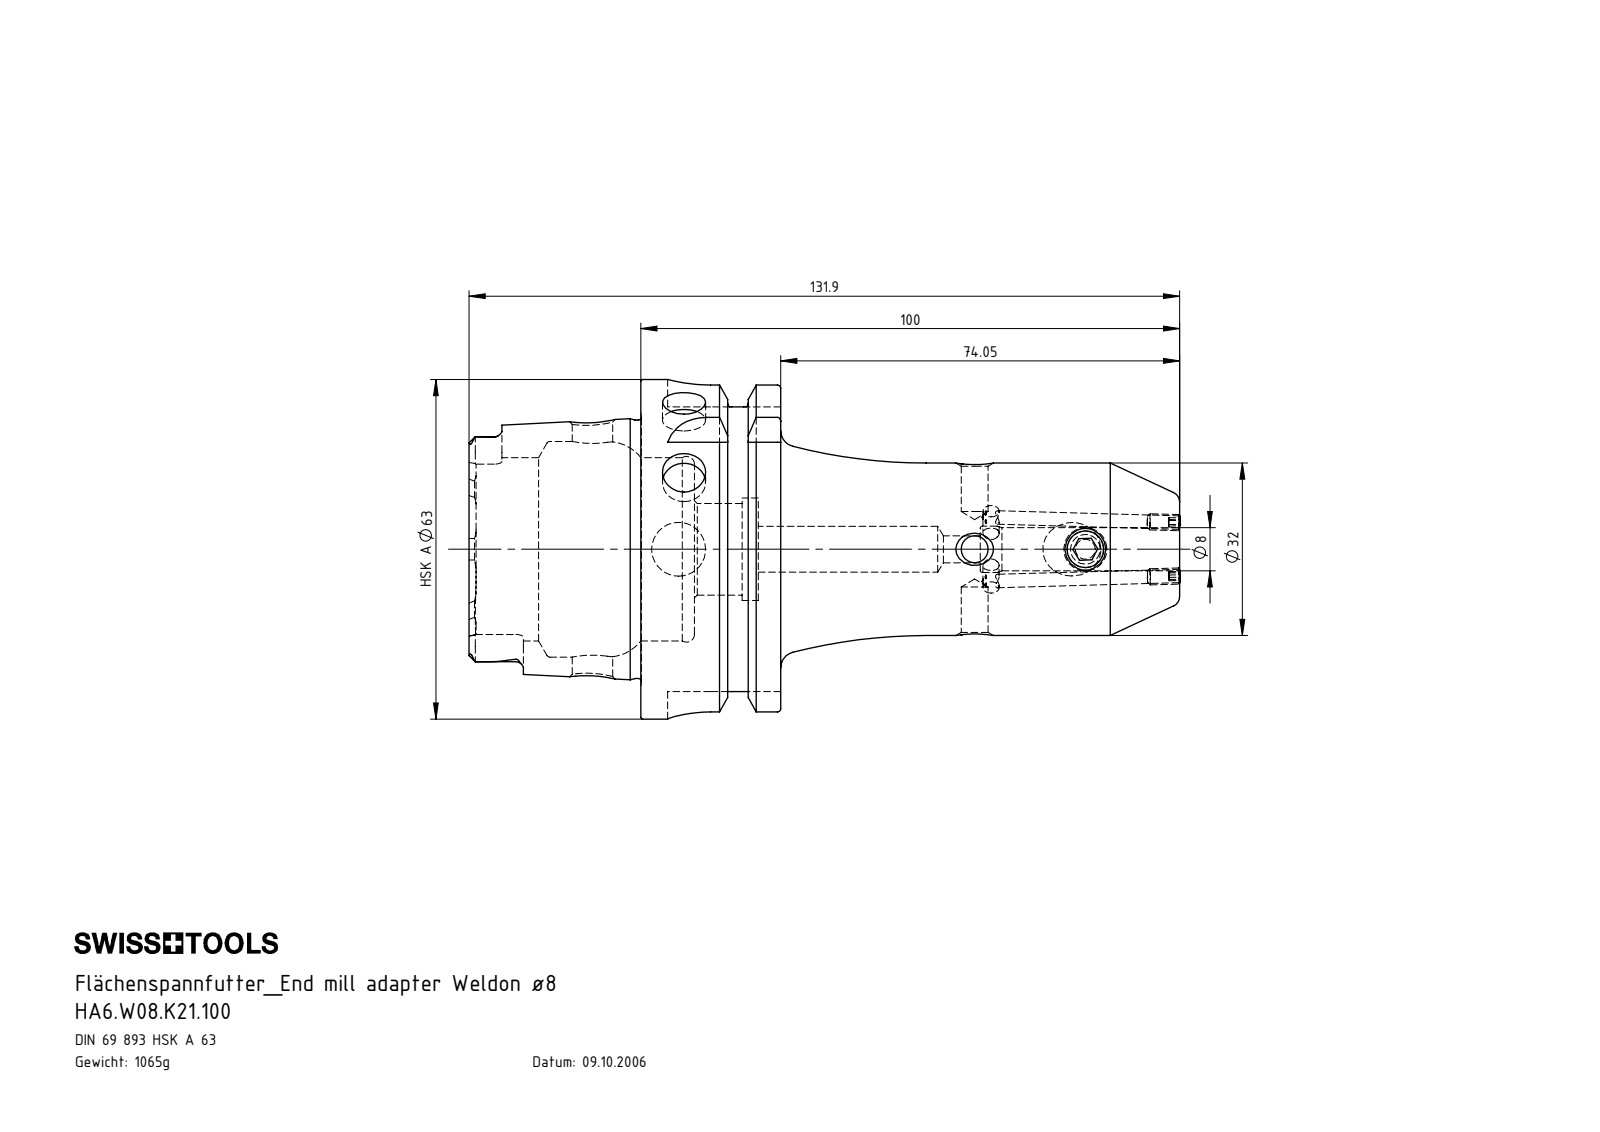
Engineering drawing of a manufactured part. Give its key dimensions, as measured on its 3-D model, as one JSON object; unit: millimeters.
{"part_name": "HA6-W08.K21.100; ERU-CJ2.001.006; W08-ER1.001.010; HA6-W08.K21.100_C_Fertigbearbeitung", "step_written_by": "SolidWorks 2012 (AUTOMOTIVE_DESIGN)", "units": "millimeters", "bodies": {"solids": 4, "faces": 292, "planar": 77, "cylindrical": 83, "other": 132}, "overall_size": [131.98, 63, 63], "volume_mm3": 135681, "surface_area_mm2": 32811, "round_holes": [[5, 3], [8, 3], [2.5, 2], [3, 1], [6.8, 1], [7.5, 1], [8.5, 1], [8.6, 1], [10, 1], [17, 1], [19, 1], [34, 1]], "round_bosses_or_shafts": [[3, 2], [63, 1], [54.95, 1], [47.94, 1], [32, 1], [8, 1]], "partial_cylinders_radius": [[1.4, 6], [2.88, 4], [8, 4]], "face_to_face_distances": [25.95, 16, 9.95, 31.9, 41.85, 57.85, 52.8, 21.8, 11.85, 53.7], "hole_center_spacings": [20.55, 54.95, 70.95, 75.5]}
